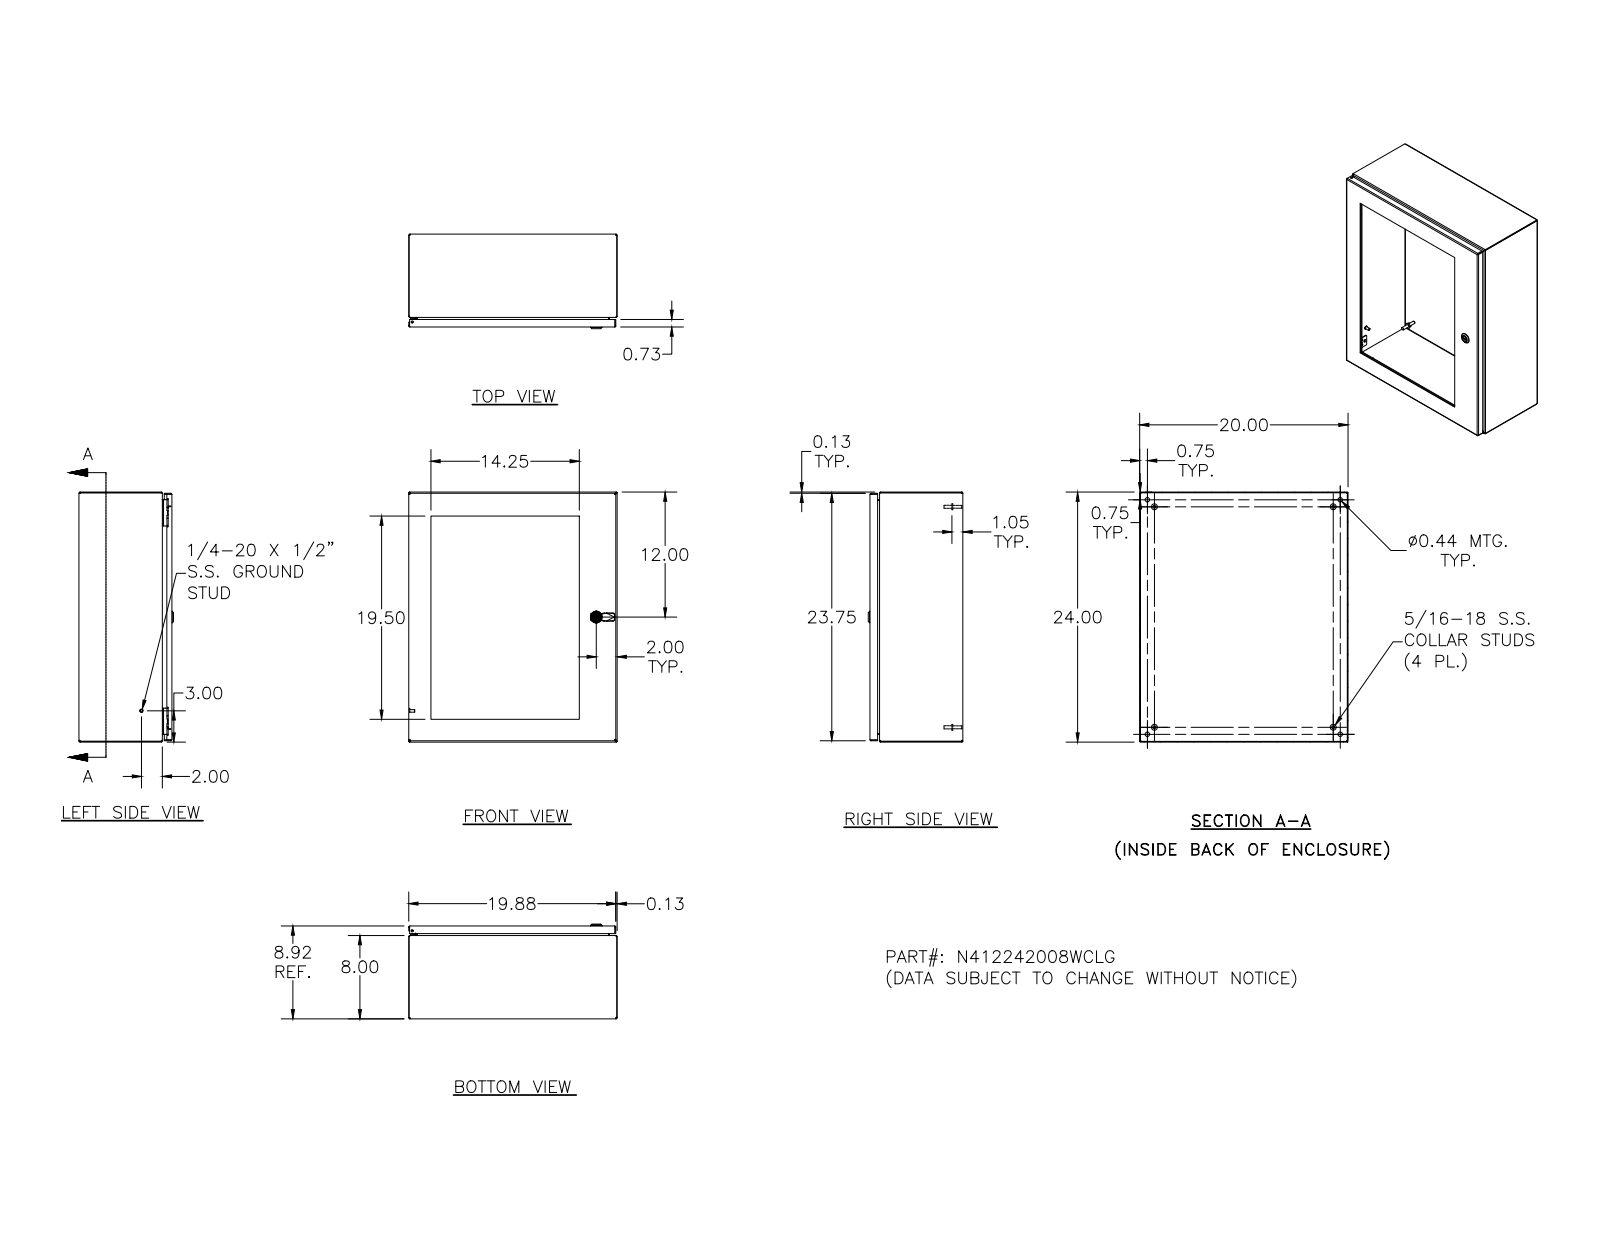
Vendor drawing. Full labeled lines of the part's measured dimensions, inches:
Part name (STEP PRODUCT): N412242008WCLG
STEP written by: SolidWorks 2018 (AUTOMOTIVE_DESIGN)
Units: inches
Bodies: 73 solids, 2083 faces (775 planar, 625 cylindrical, 683 other)
Overall size (bounding box): 24 × 20 × 9.075
Volume: 199.9 in³ · Surface area: 3 972 in²
Round holes (diameter × count): ⌀0.156 ×20, ⌀0.281 ×18, ⌀0.188 ×5, ⌀0.093 ×4, ⌀0.152 ×4, ⌀0.167 ×4, ⌀0.172 ×4, ⌀0.437 ×4, ⌀0.187 ×1, ⌀0.197 ×1, ⌀0.315 ×1, ⌀0.394 ×1
Round bosses / shafts (diameter × count): ⌀0.337 ×18, ⌀0.19 ×18, ⌀0.25 ×10, ⌀0.563 ×4, ⌀0.36 ×4, ⌀0.32 ×4, ⌀0.3 ×4, ⌀0.275 ×4
Partial cylindrical surfaces — rounded edges, fillets, slot ends (radius × count): R0.031 ×34, R0.012 ×30, R0.05 ×26, R0.105 ×24, R0.016 ×18, R0.125 ×16, R0.02 ×13, R0.032 ×8
Main face-to-face distances: 0.074, 8.843, 8.769, 19.926, 0.25, 8.593, 8.519, 23.926, 19.852, 20
Hole centre spacings: 4, 8, 16.008, 12, 17.443, 20, 21.132, 15.5
